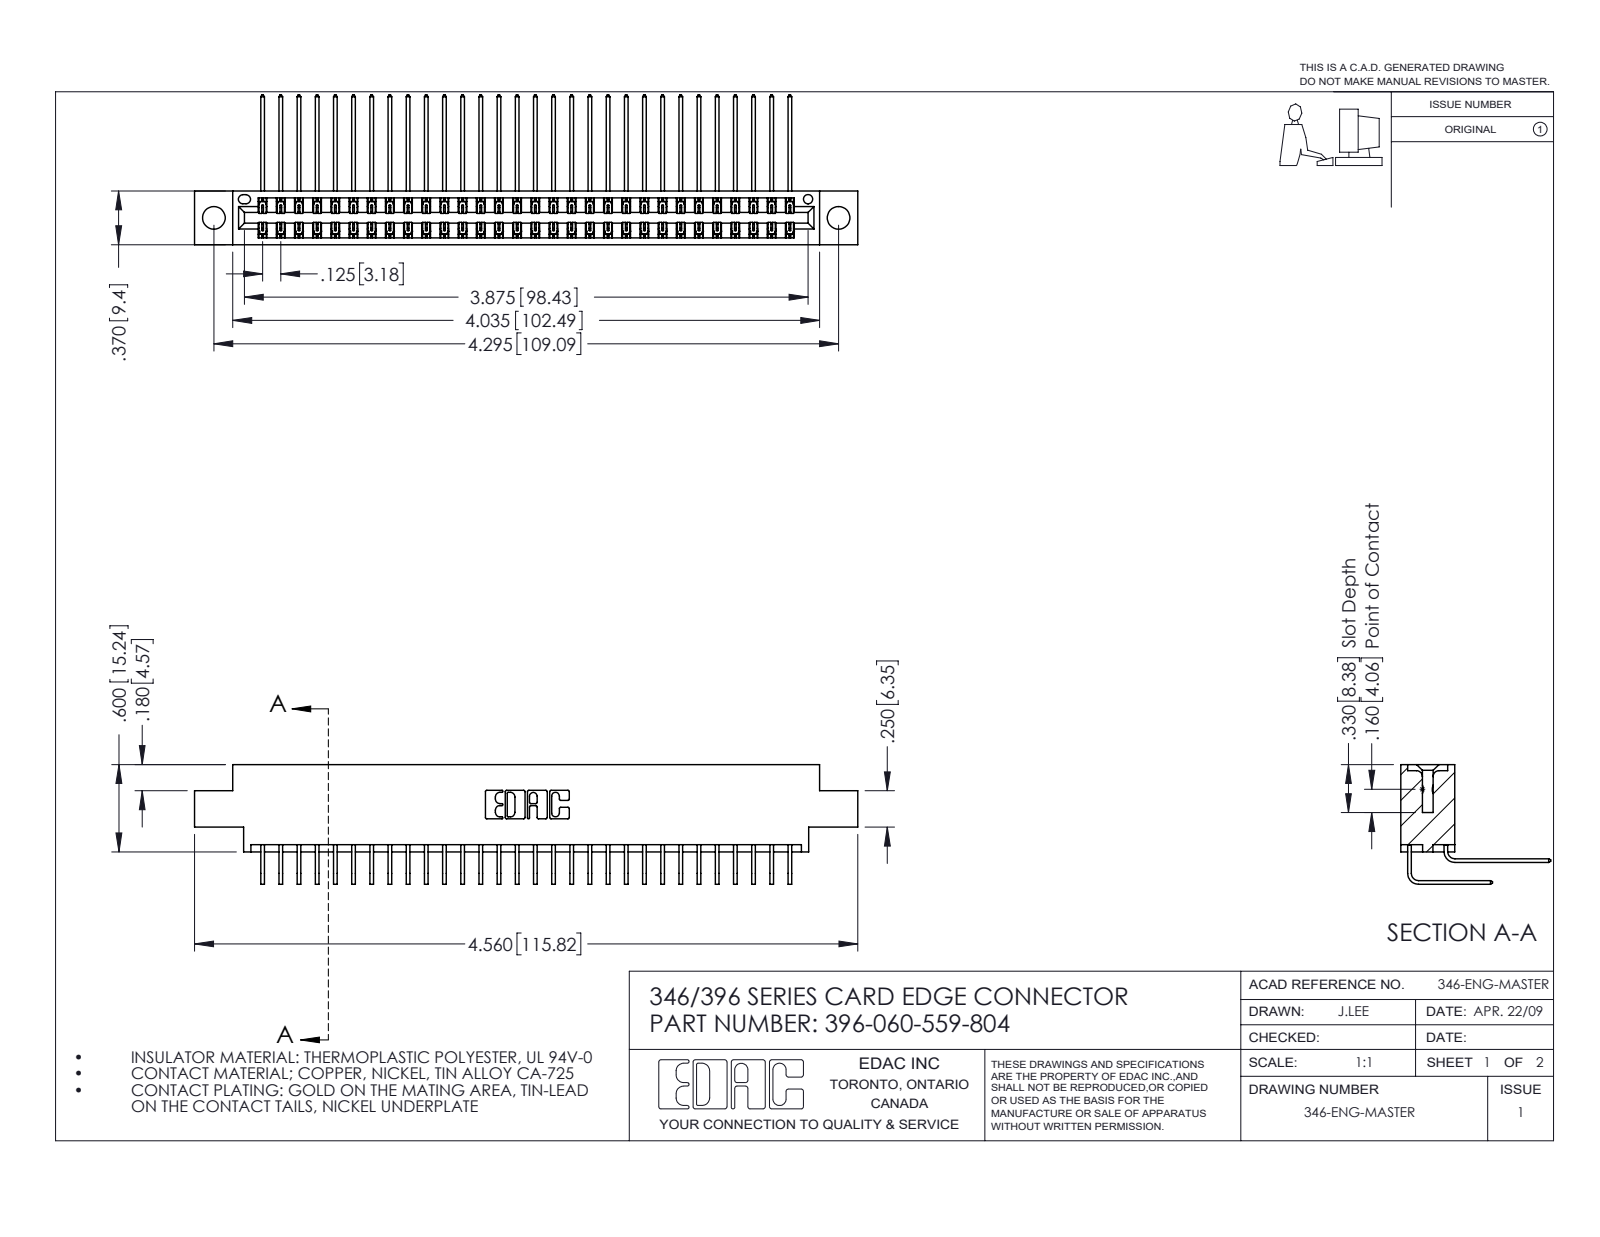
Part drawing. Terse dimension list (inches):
name: 396-060-559-804; 345-292-001_558 559 Tail - 1; 345-292-001_559 Tail - 2; 346 Part_0.170 Offset - 0.156 Dia-TH
written by: SolidWorks 2016 (CONFIG_CONTROL_DESIGN)
unit: in
bodies: 61 solids, 3366 faces (2300 planar, 1066 cylindrical, 0 other)
size: 4.56 × 1.03 × 0.823
volume: 0.69 in³; area: 26.36 in²
holes: 2× ⌀0.156, 1× ⌀0.064
rounds: 90× R0.006, 22× R0.01, 6× R0.007, 6× R0.031, 3× R0.026, 2× R0.014, 2× R0.022, 2× R0.024
face distances: 0.048, 0.322, 0.025, 0.37, 0.25, 0.072, 0.298, 0.275, 0.148, 0.222
hole spacings: 0.246, 4.087, 4.295
